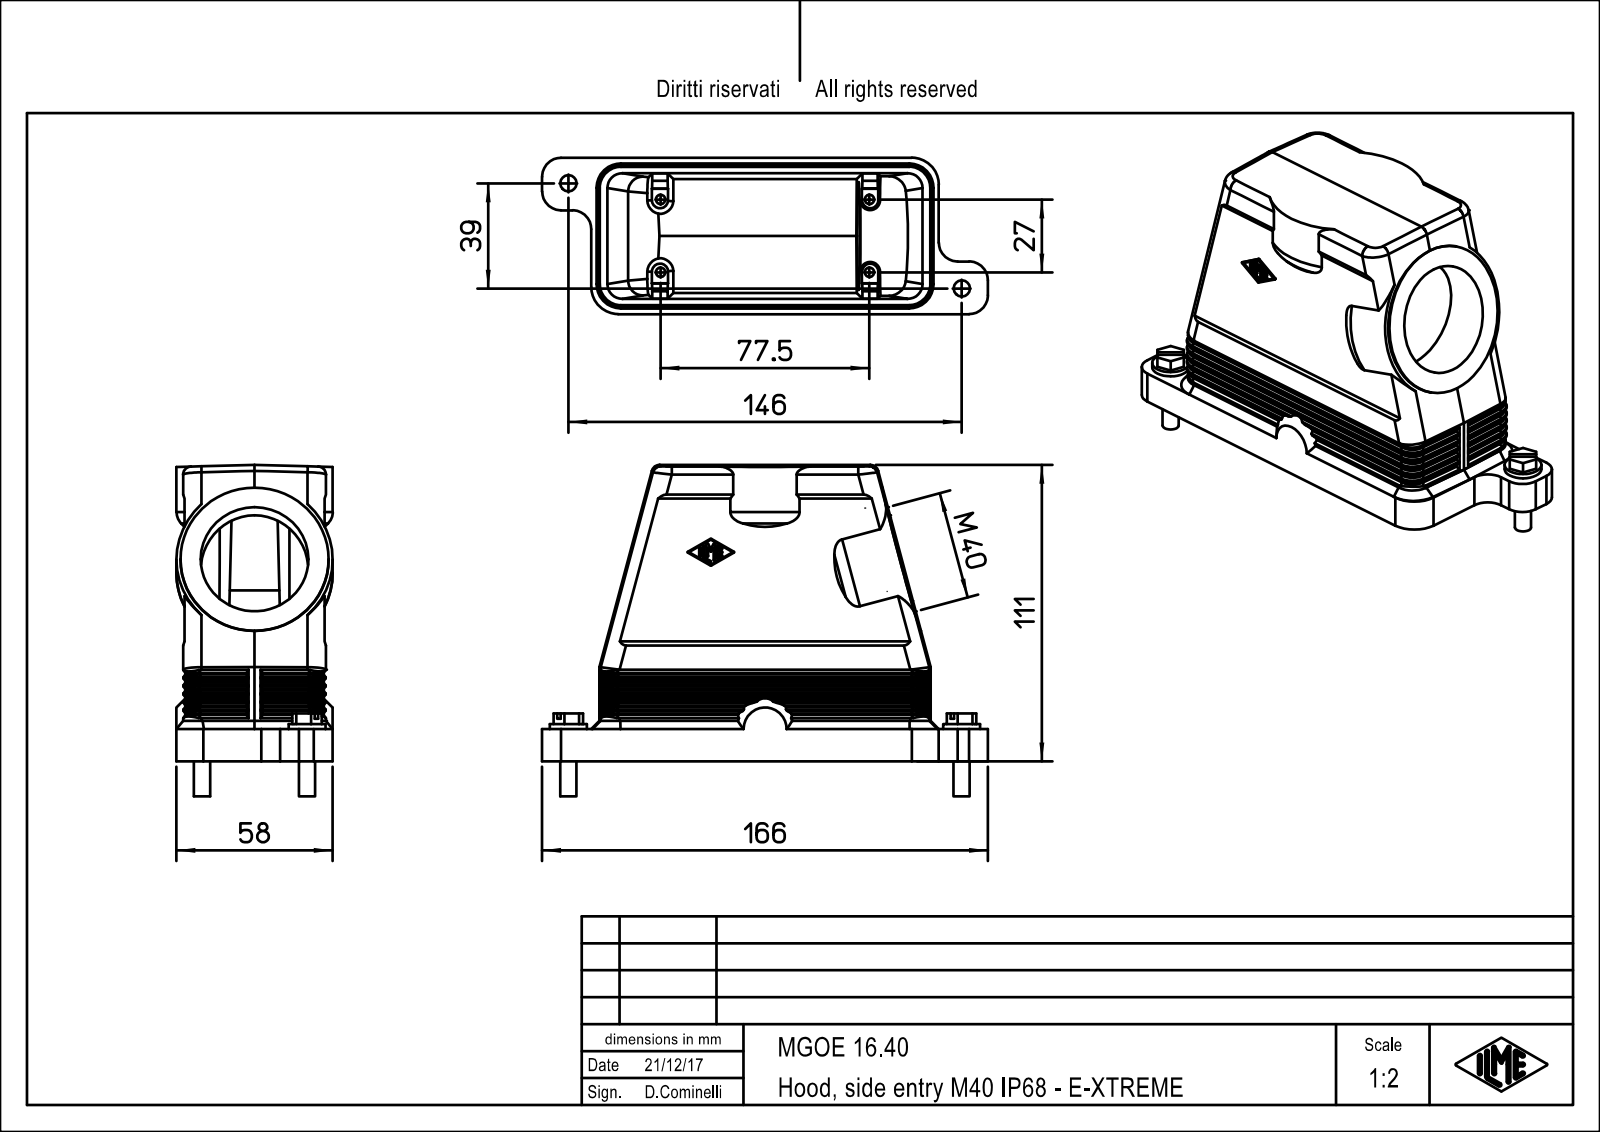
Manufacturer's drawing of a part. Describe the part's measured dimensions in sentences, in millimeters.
The part is named "MGOE_16.40". Its 3-D file was written by "PTC Creo Elements/Direct Modeling 19.0E 27-Jun-2016 (C) Parametric Technology GmbH (AUTOMOTIVE_DESIGN)". It is 1 solid with 534 faces: 254 planar, 124 cylindrical and 156 other. Overall it measures 165.5 by 123 by 58 millimeters. Its volume is 192 242 cubic millimeters and its surface area 83 228 square millimeters. Round holes: 4 of diameter 3.5, 1 of diameter 40. Round bosses or shafts: 2 of diameter 13.7, 2 of diameter 6, 1 of diameter 55. Partial cylindrical surfaces (rounded edges, fillets, slot ends): 62 of radius 7, 15 of radius 0.33, 6 of radius 5.5, 4 of radius 8.5, 2 of radius 0.17, 2 of radius 10, 2 of radius 29, 1 of radius 0.17. The main face-to-face distances are 52, 3, 55, 2.5, 0.5, 55.5, 52.5, 3.33, 78, 58. The hole center spacings are 27, 77.5, 82.07.
